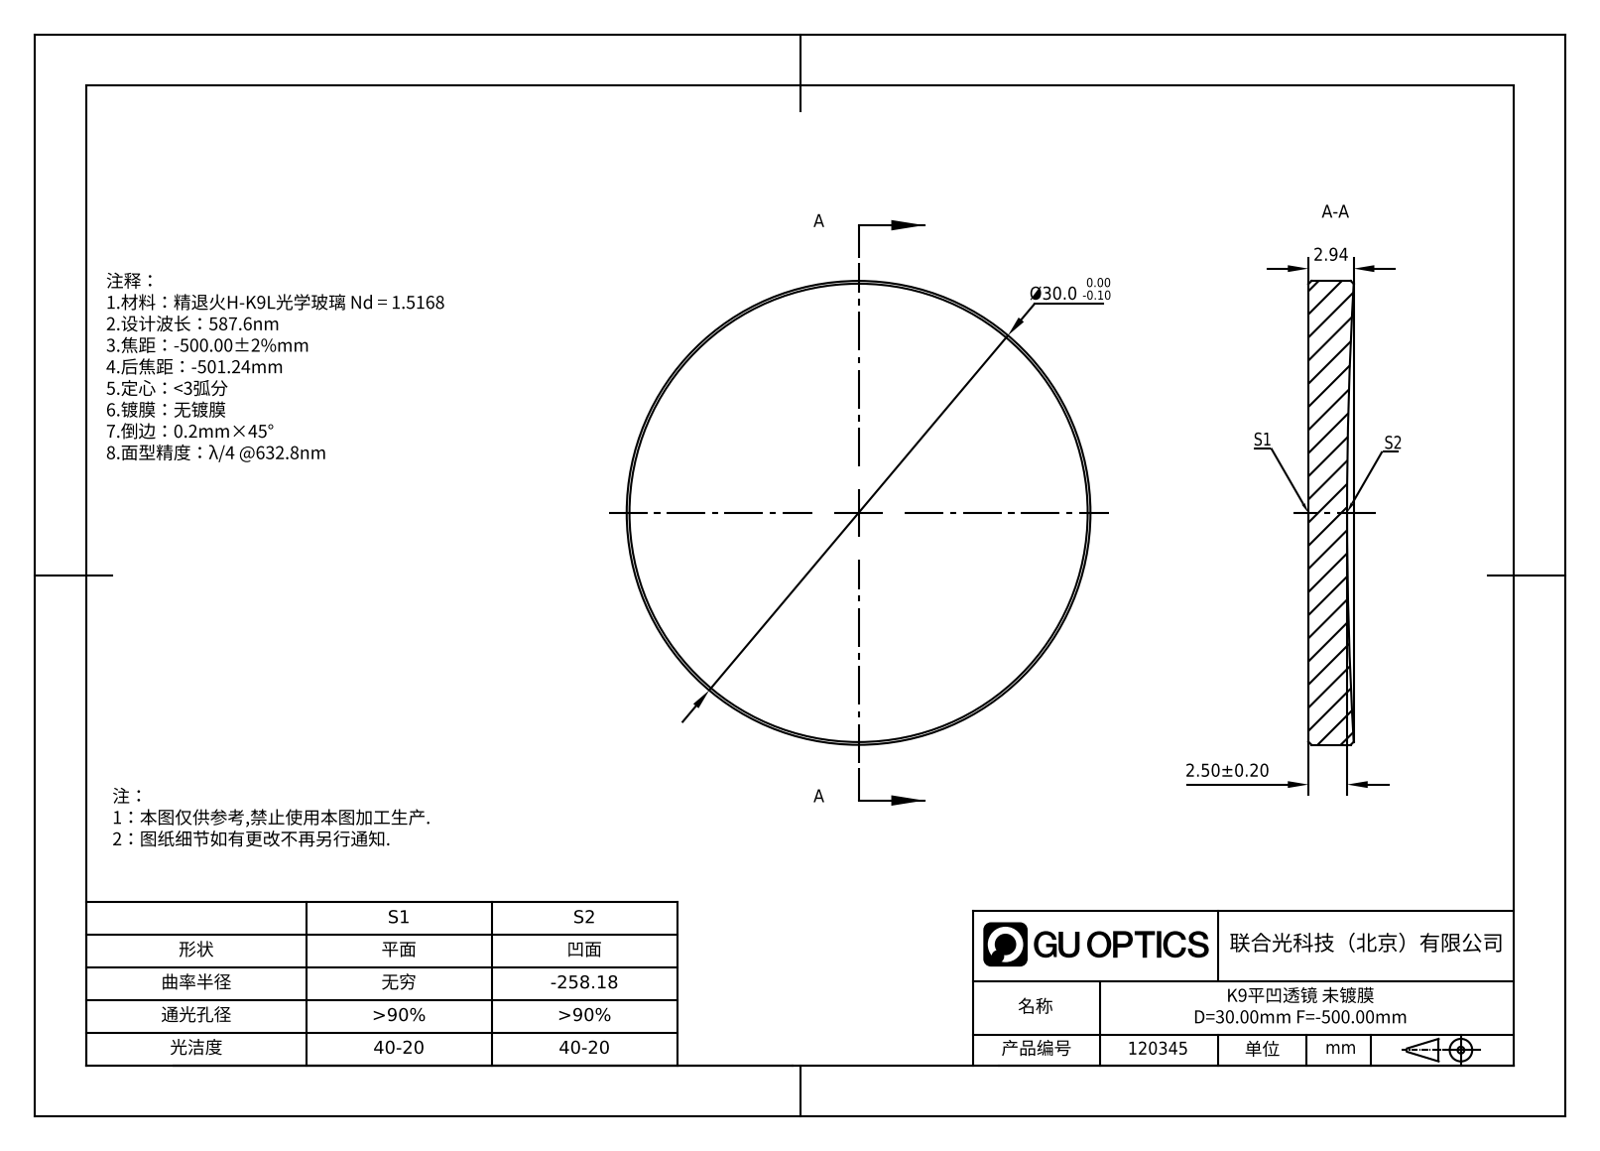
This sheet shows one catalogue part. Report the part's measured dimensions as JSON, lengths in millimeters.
{"part_name": "GL13-030-500", "step_written_by": "SolidWorks 2022 (AUTOMOTIVE_DESIGN)", "units": "millimeters", "bodies": {"solids": 1, "faces": 9, "planar": 1, "cylindrical": 2, "other": 6}, "overall_size": [30, 30, 2.93], "volume_mm3": 1919, "surface_area_mm2": 1669, "round_bosses_or_shafts": [[30, 1]]}
